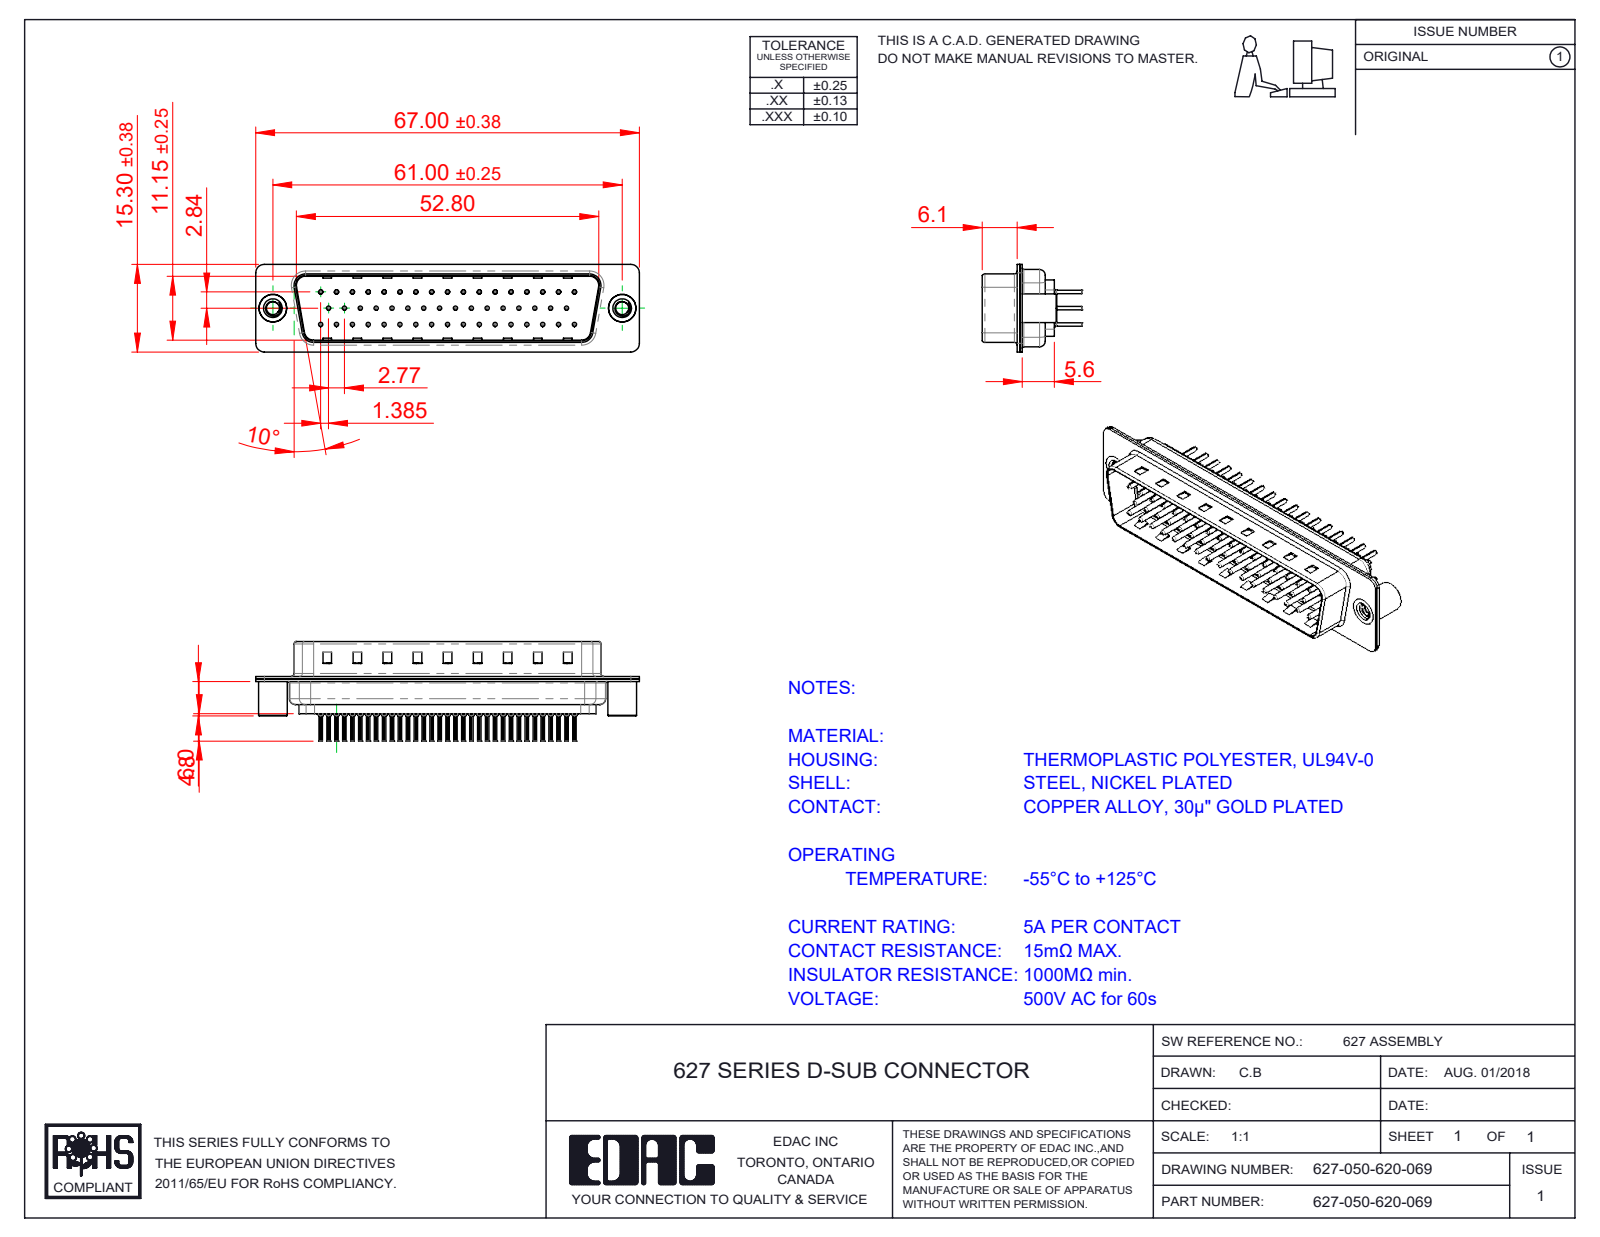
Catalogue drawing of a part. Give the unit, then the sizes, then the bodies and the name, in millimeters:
Units: millimetres
Overall size (bounding box): 67 × 17.3 × 15.3
Round holes (diameter × count): ⌀0.2 ×50, ⌀0.35 ×50, ⌀1.1 ×50, ⌀1.6 ×50, ⌀2.26 ×2, ⌀4 ×2, ⌀4.8 ×2
Round bosses / shafts (diameter × count): ⌀2 ×50, ⌀1.5 ×50, ⌀0.75 ×50, ⌀0.6 ×50, ⌀5 ×2, ⌀4.9 ×2
Partial cylindrical surfaces — rounded edges, fillets, slot ends (radius × count): R0.1 ×100, R1.5 ×16, R2 ×12, R0.5 ×8, R1.6 ×8, R0.25 ×4, R0.6 ×4, R0.65 ×4
Main face-to-face distances: 0.4, 0.45, 11.55, 0.9, 6.05, 6.5, 0.78, 12.33, 1.95, 0.77
Hole centre spacings: 3.16, 2.77, 5.54, 8.31, 11.08, 13.85, 16.62, 5.03
Volume: 4 520 mm³ · Surface area: 12 775 mm²
Bodies: 55 solids, 5334 faces (1403 planar, 2011 cylindrical, 1920 other)
Part name (STEP PRODUCT): 627 Shell Front_50 Contacts; 627 Contact Row 3_20L; 627 Housing_50 LP; 627-050-620-069 (+4 more)
STEP written by: SolidWorks 2020 (CONFIG_CONTROL_DESIGN)
